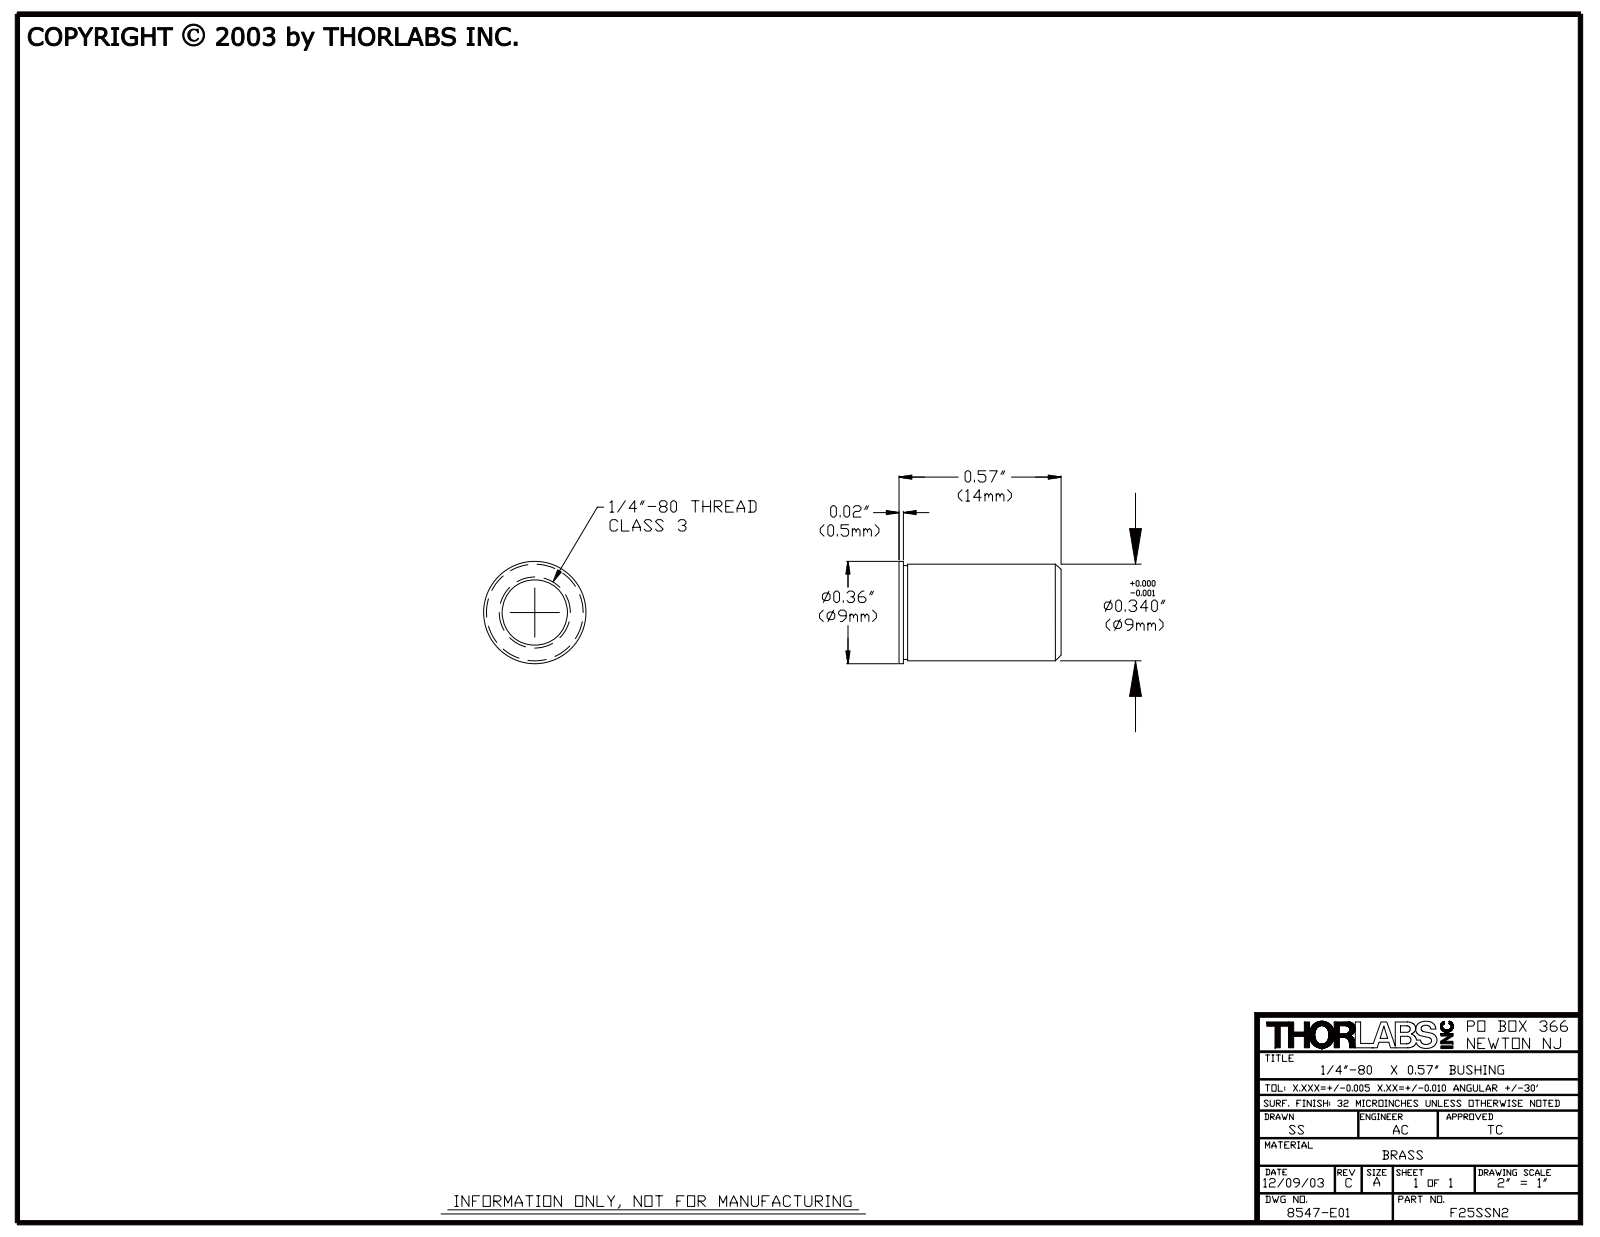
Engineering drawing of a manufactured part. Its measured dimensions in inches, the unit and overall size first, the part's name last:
Units: inches
Overall size (bounding box): 0.57 × 0.36 × 0.36
Round holes (diameter × count): ⌀0.25 ×1
Round bosses / shafts (diameter × count): ⌀0.36 ×1, ⌀0.34 ×1, ⌀0.3 ×1
Main face-to-face distances: 0.02, 0.04, 0.57, 0.55, 0.53
Bodies: 0 solids, 18 faces (4 planar, 8 cylindrical, 6 other)
Part name (STEP PRODUCT): 8547-E0W
STEP written by: SolidWorks 2007 (AUTOMOTIVE_DESIGN)
